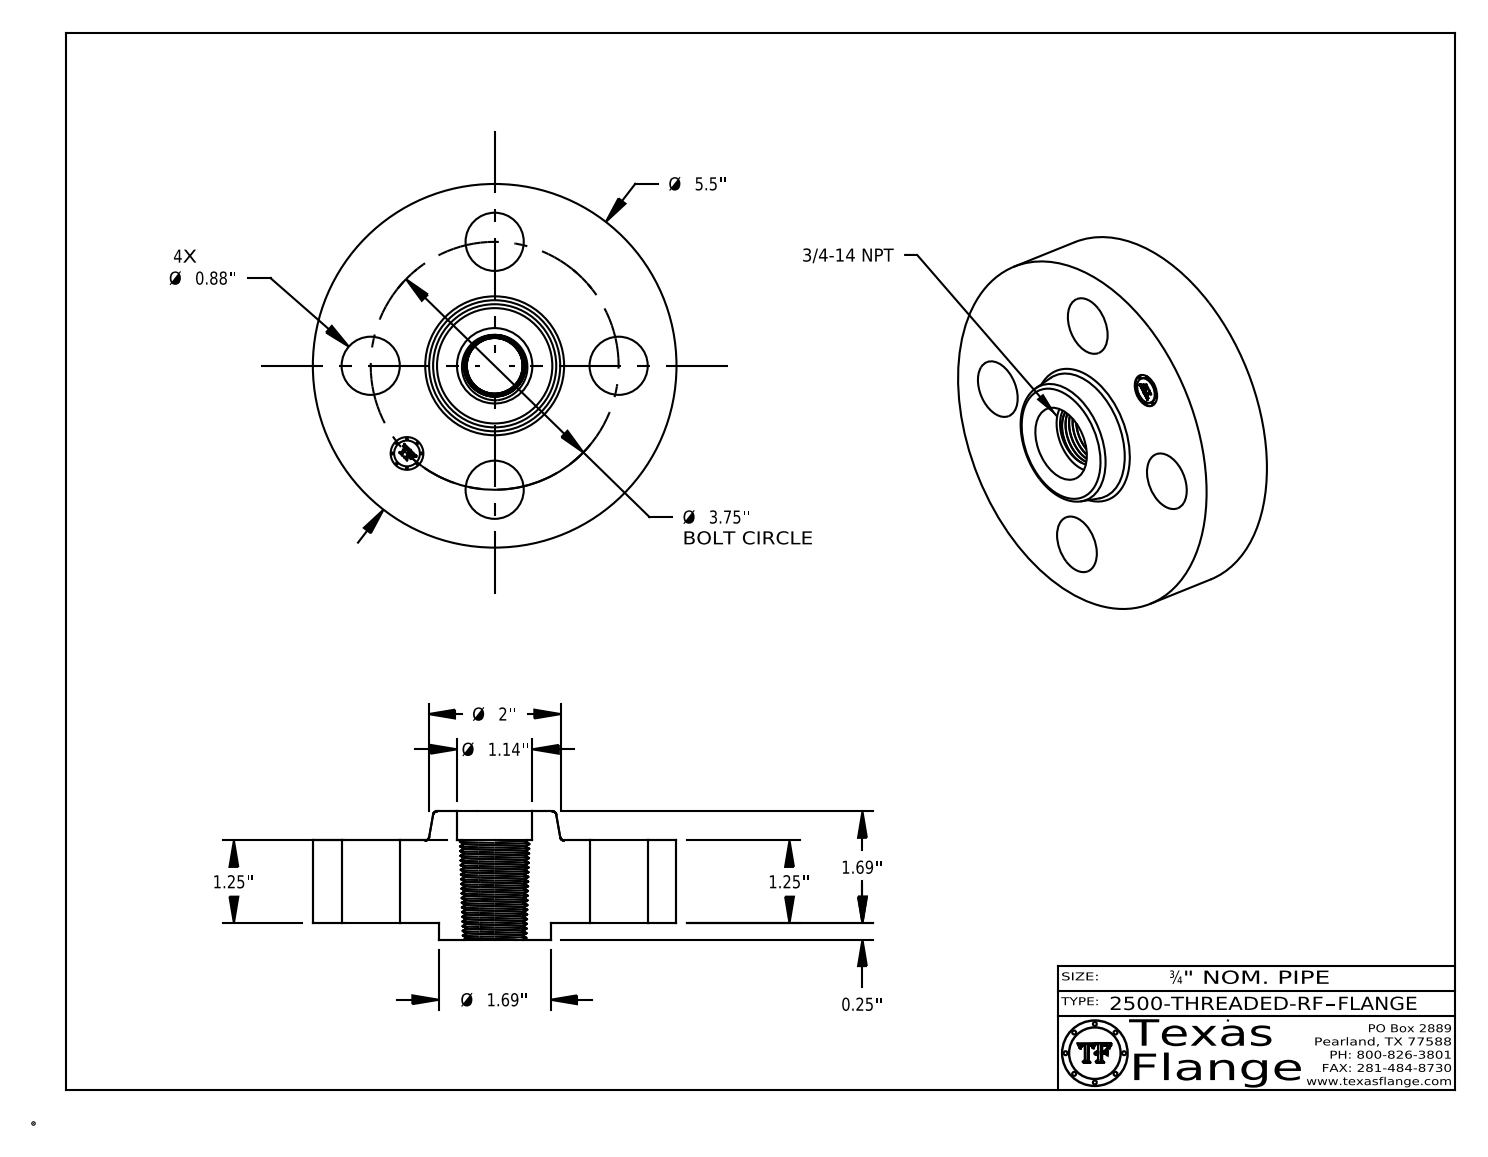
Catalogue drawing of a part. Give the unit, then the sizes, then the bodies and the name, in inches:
Units: inches
Overall size (bounding box): 5.5 × 5.5 × 1.94
Round holes (diameter × count): ⌀0.88 ×4, ⌀0.495 ×1, ⌀1.14 ×1
Round bosses / shafts (diameter × count): ⌀0.03 ×8, ⌀5.5 ×1, ⌀1.69 ×1, ⌀0.39 ×1
Main face-to-face distances: 1.25, 0.25, 1.5, 1.94, 1.69, 0.44, 1.485, 1.235, 0.015, 0.455
Hole centre spacings: 1.875, 2.652, 1.435, 3.465, 3.75
Volume: 27 in³ · Surface area: 90.01 in²
Bodies: 1 solid, 628 faces (370 planar, 34 cylindrical, 224 other)
Part name (STEP PRODUCT): 2500-THREADED-RF
STEP written by: CATIA V5 STEP AP214 (AUTOMOTIVE_DESIGN)
